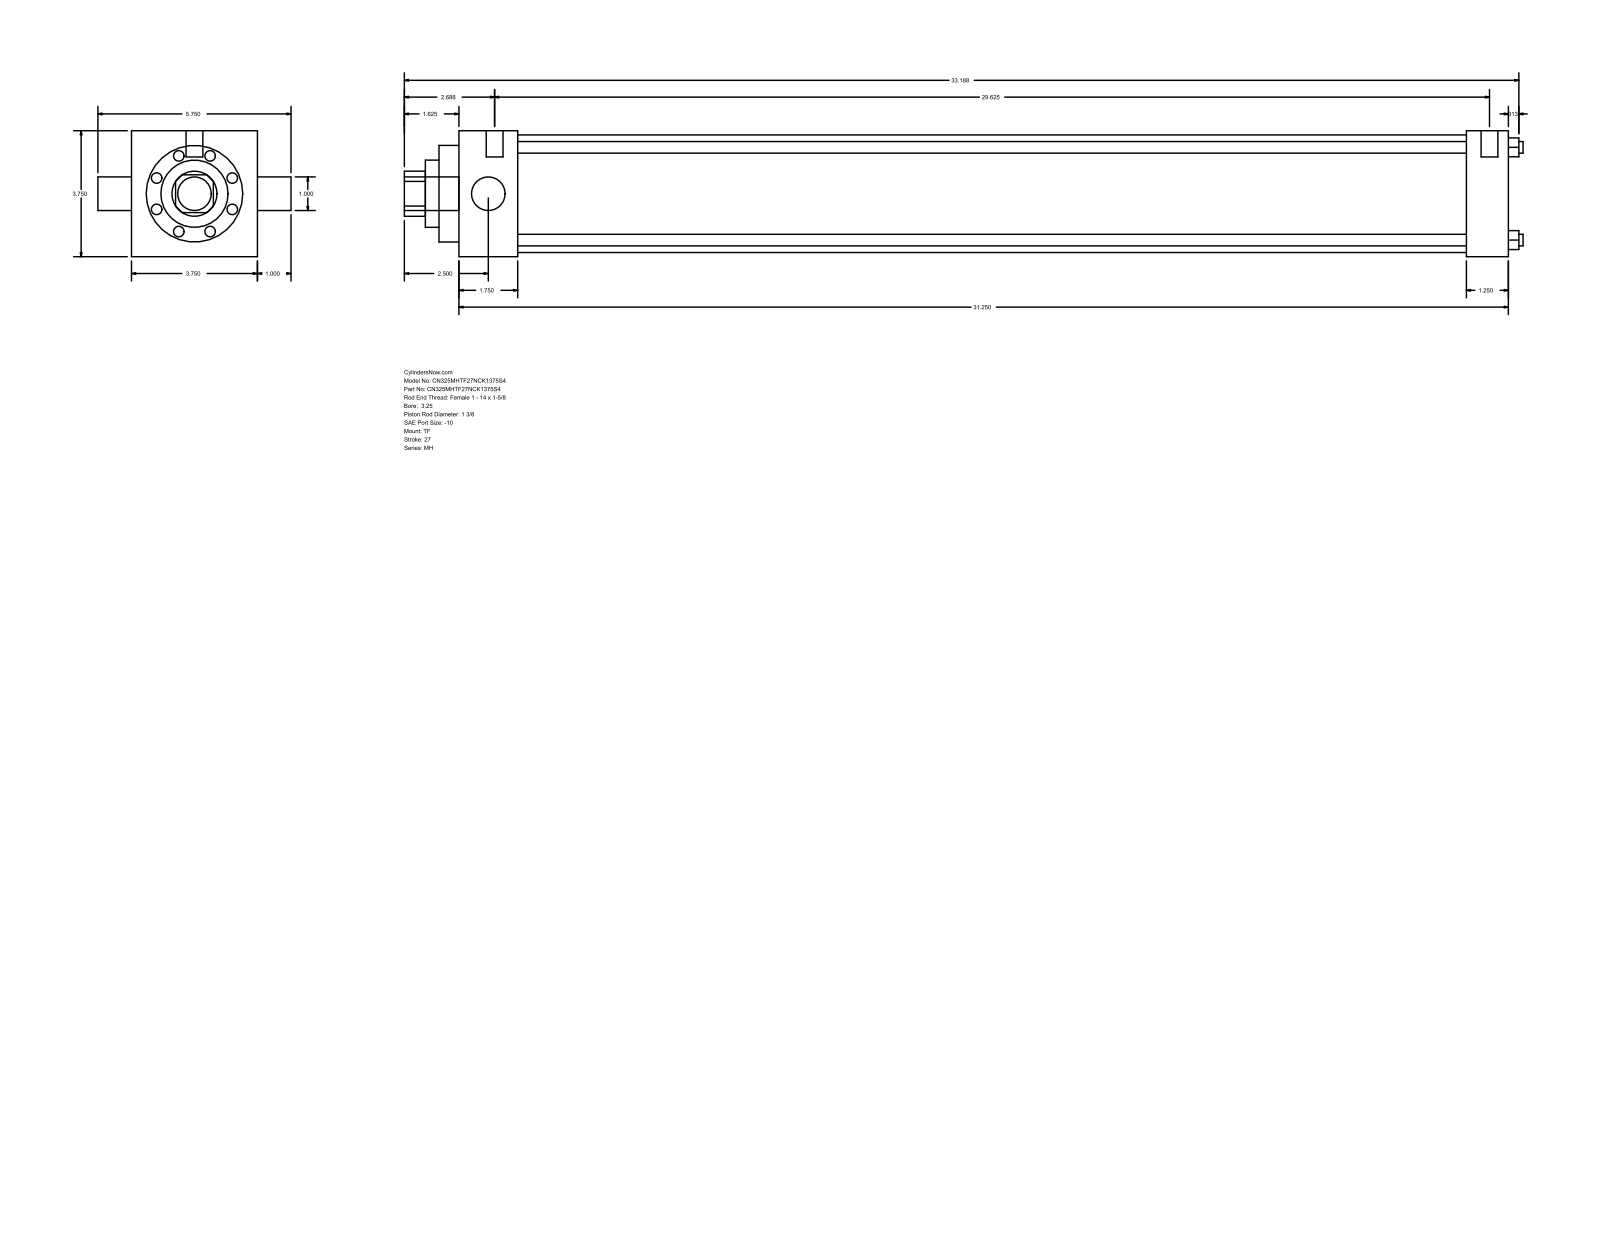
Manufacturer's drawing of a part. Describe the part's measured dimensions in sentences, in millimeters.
The part is named "MH_TF__0325_1.375". Its 3-D file was written by "GSSL Pune (CONFIG_CONTROL_DESIGN)". It is 0 solids with 86 faces: 61 planar, 25 cylindrical and 0 other. Overall it measures 846.14 by 146.05 by 95.25 millimeters. Round holes: 4 of diameter 8.76, 1 of diameter 25.4, 1 of diameter 34.92, 1 of diameter 50.8, 1 of diameter 73.03, 1 of diameter 88.9. Round bosses or shafts: 3 of diameter 5.56, 2 of diameter 12.7, 1 of diameter 25.4. Partial cylindrical surfaces (rounded edges, fillets, slot ends): 1 of radius 17.06. The main face-to-face distances are 95.24, 793.75, 44.45, 762, 717.55, 749.3, 31.75, 15.08, 59.53, 777.08. The hole center spacings are 49.57, 70.1, 99.14.
